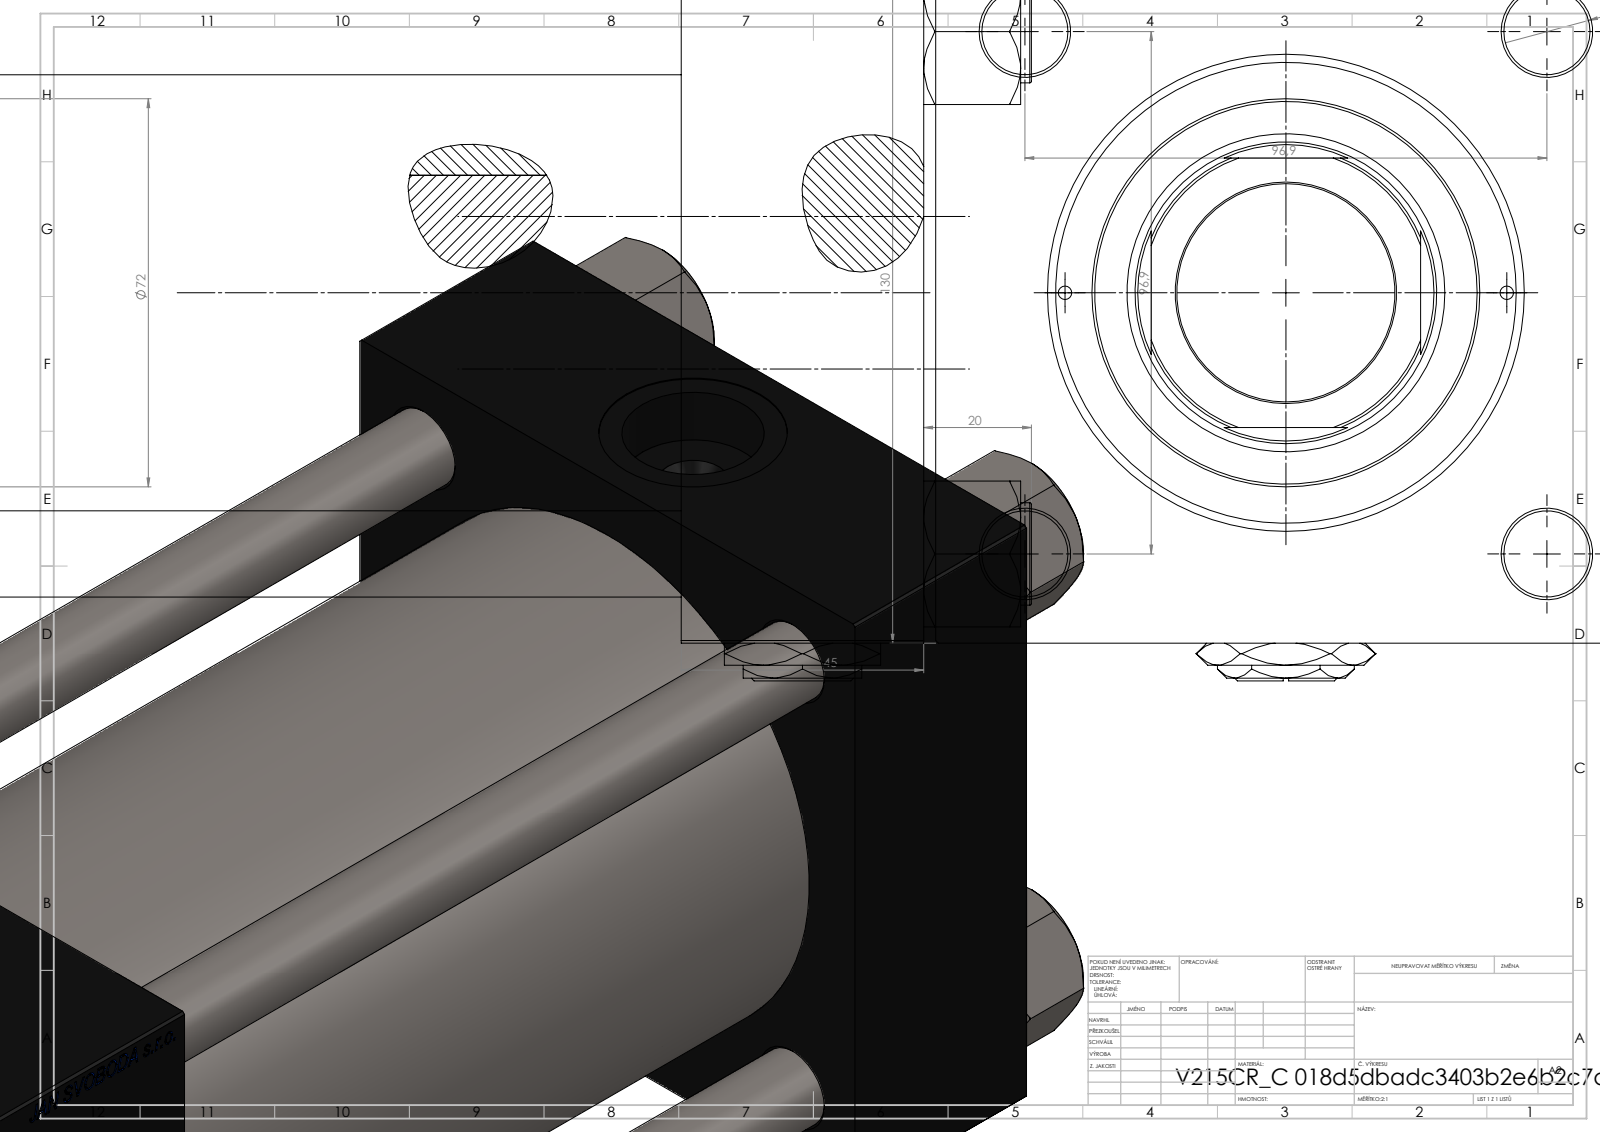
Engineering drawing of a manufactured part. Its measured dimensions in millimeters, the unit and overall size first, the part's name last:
Units: millimetres
Overall size (bounding box): 348 × 137 × 130
Round holes (diameter × count): ⌀16 ×4, ⌀2.5 ×2, ⌀7 ×2, ⌀26.44 ×2, ⌀35 ×2, ⌀40.5 ×1, ⌀56 ×1, ⌀59 ×1, ⌀76 ×1, ⌀85.5 ×1, ⌀100 ×1
Round bosses / shafts (diameter × count): ⌀19 ×4, ⌀106 ×1, ⌀72 ×1
Partial cylindrical surfaces — rounded edges, fillets, slot ends (radius × count): R27 ×1
Main face-to-face distances: 130, 45, 293, 248, 221, 176, 72, 51, 125, 197
Hole centre spacings: 49.02, 68.52, 96.9, 101.73, 41, 137.04, 82, 223.5
Volume: 2 905 000 mm³ · Surface area: 448 200 mm²
Bodies: 13 solids, 1303 faces (623 planar, 102 cylindrical, 578 other)
Part name (STEP PRODUCT): Zatka_pro_OIL_PORT; V215CR_C_TYCINKA; V215CR_C_Body; V215_VC_A (+2 more)
STEP written by: SolidWorks 2019 (CONFIG_CONTROL_DESIGN)
